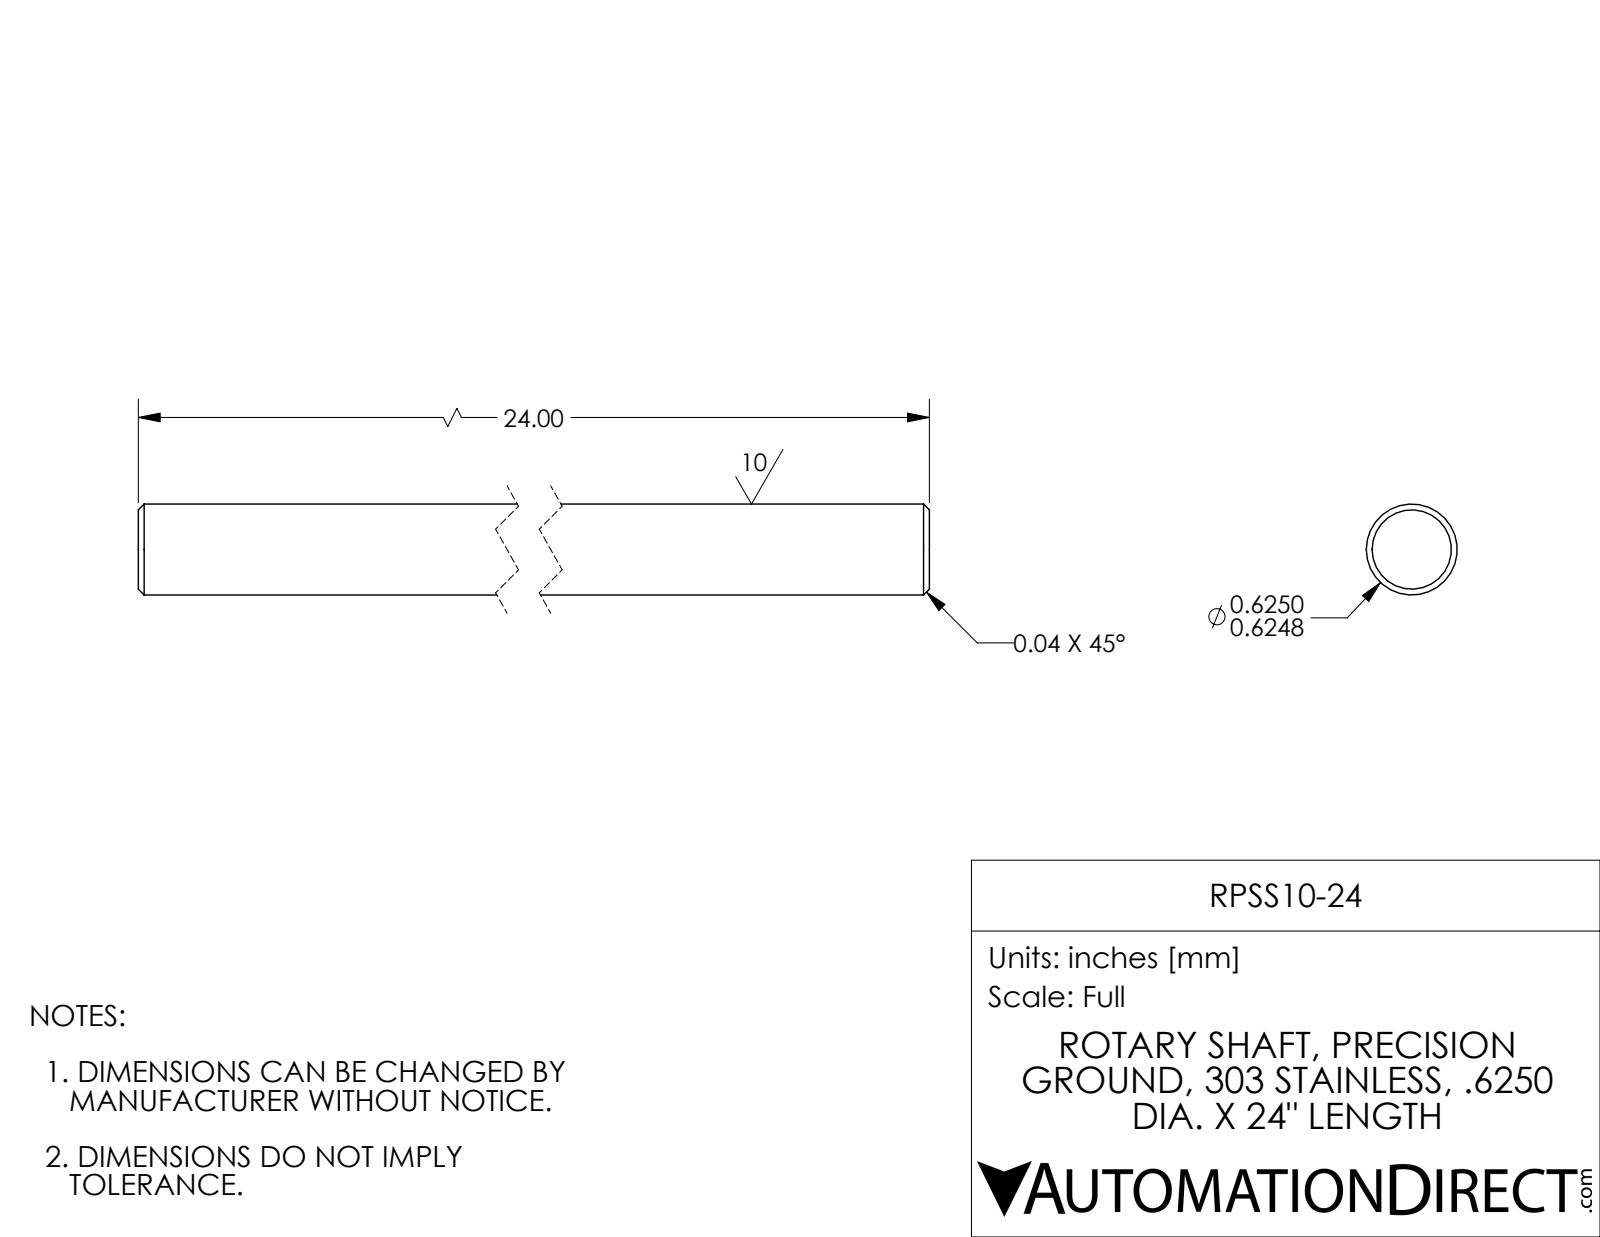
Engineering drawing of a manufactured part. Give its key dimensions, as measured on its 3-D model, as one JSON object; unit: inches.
{"part_name": "RPSS10-24", "step_written_by": "SolidWorks 2017 (AUTOMOTIVE_DESIGN)", "units": "inches", "bodies": {"solids": 1, "faces": 8, "planar": 2, "cylindrical": 2, "other": 4}, "overall_size": [24, 0.625, 0.625], "volume_in3": 7.36, "surface_area_in2": 47.64, "round_bosses_or_shafts": [[0.625, 1]], "face_to_face_distances": [24]}
